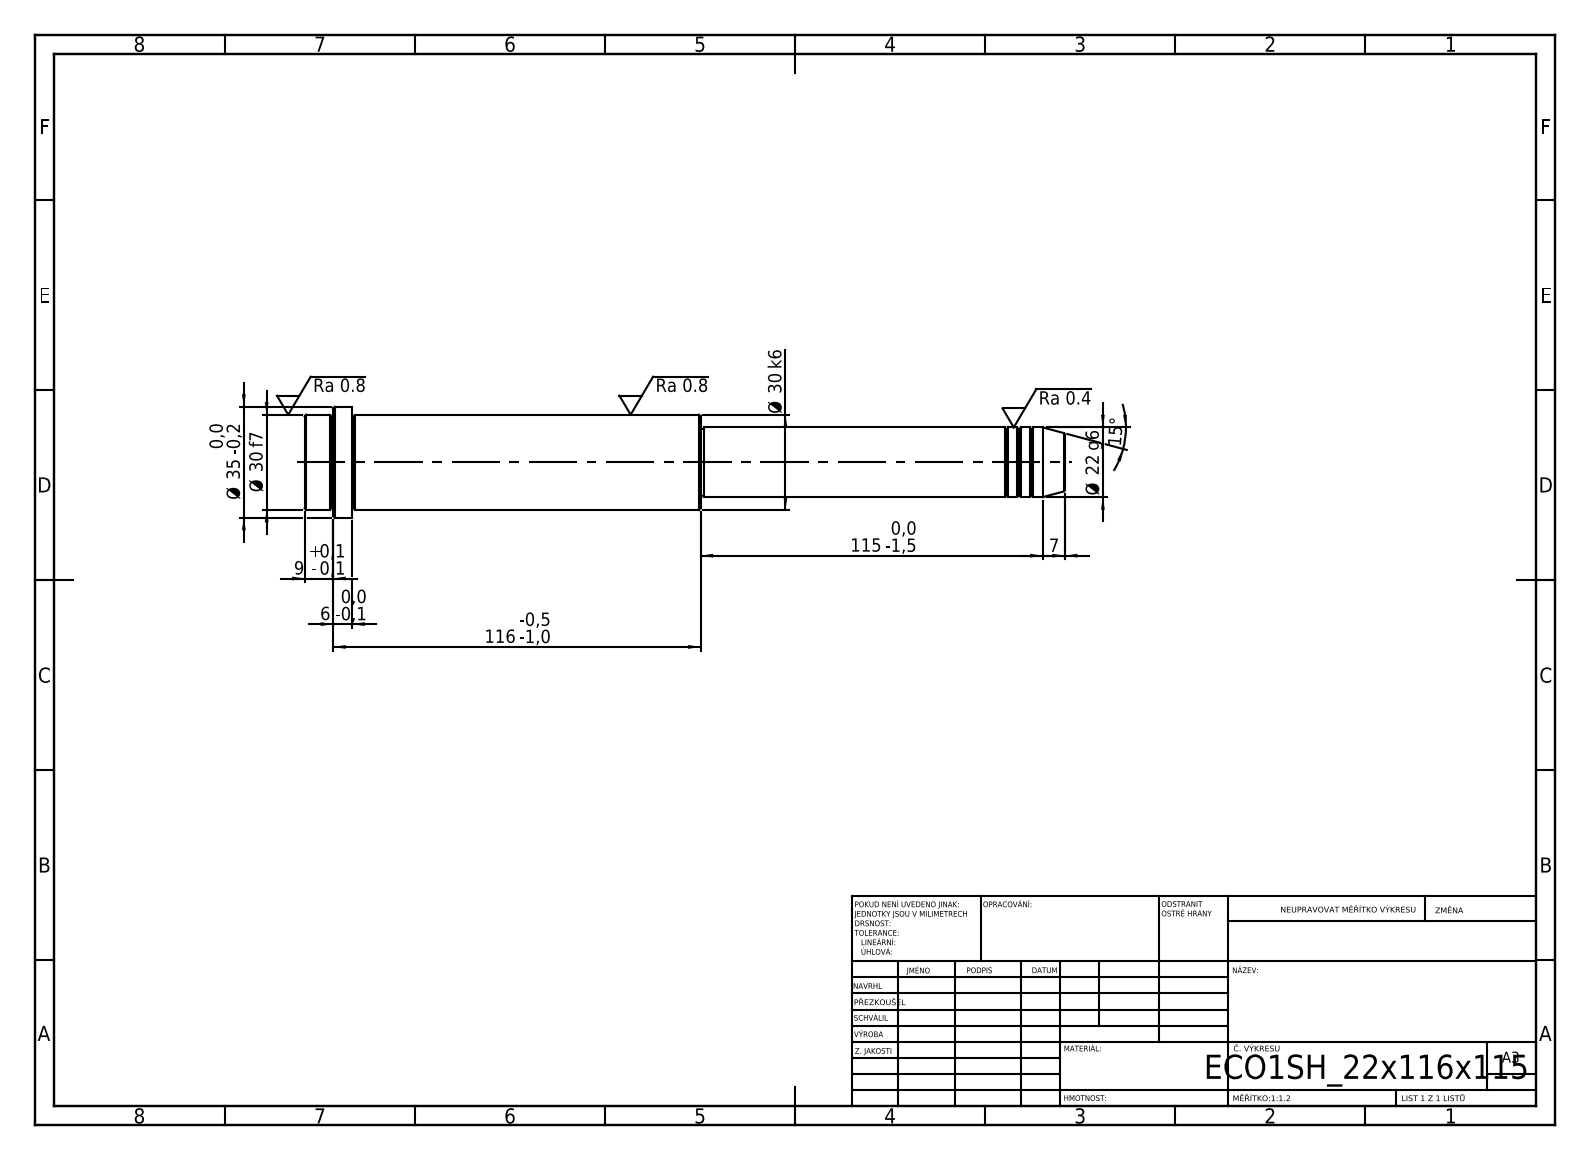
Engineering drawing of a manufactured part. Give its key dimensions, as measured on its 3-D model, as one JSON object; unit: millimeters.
{"step_written_by": "SolidWorks 2019 (CONFIG_CONTROL_DESIGN)", "units": "millimeters", "bodies": {"solids": 1, "faces": 52, "planar": 6, "cylindrical": 16, "other": 30}, "overall_size": [240, 35, 35], "volume_mm3": 132951, "surface_area_mm2": 21783, "round_bosses_or_shafts": [[35, 1], [30, 1], [22, 1], [21, 1]], "face_to_face_distances": [125, 110, 15, 115, 225, 240, 231, 116, 6, 9]}
